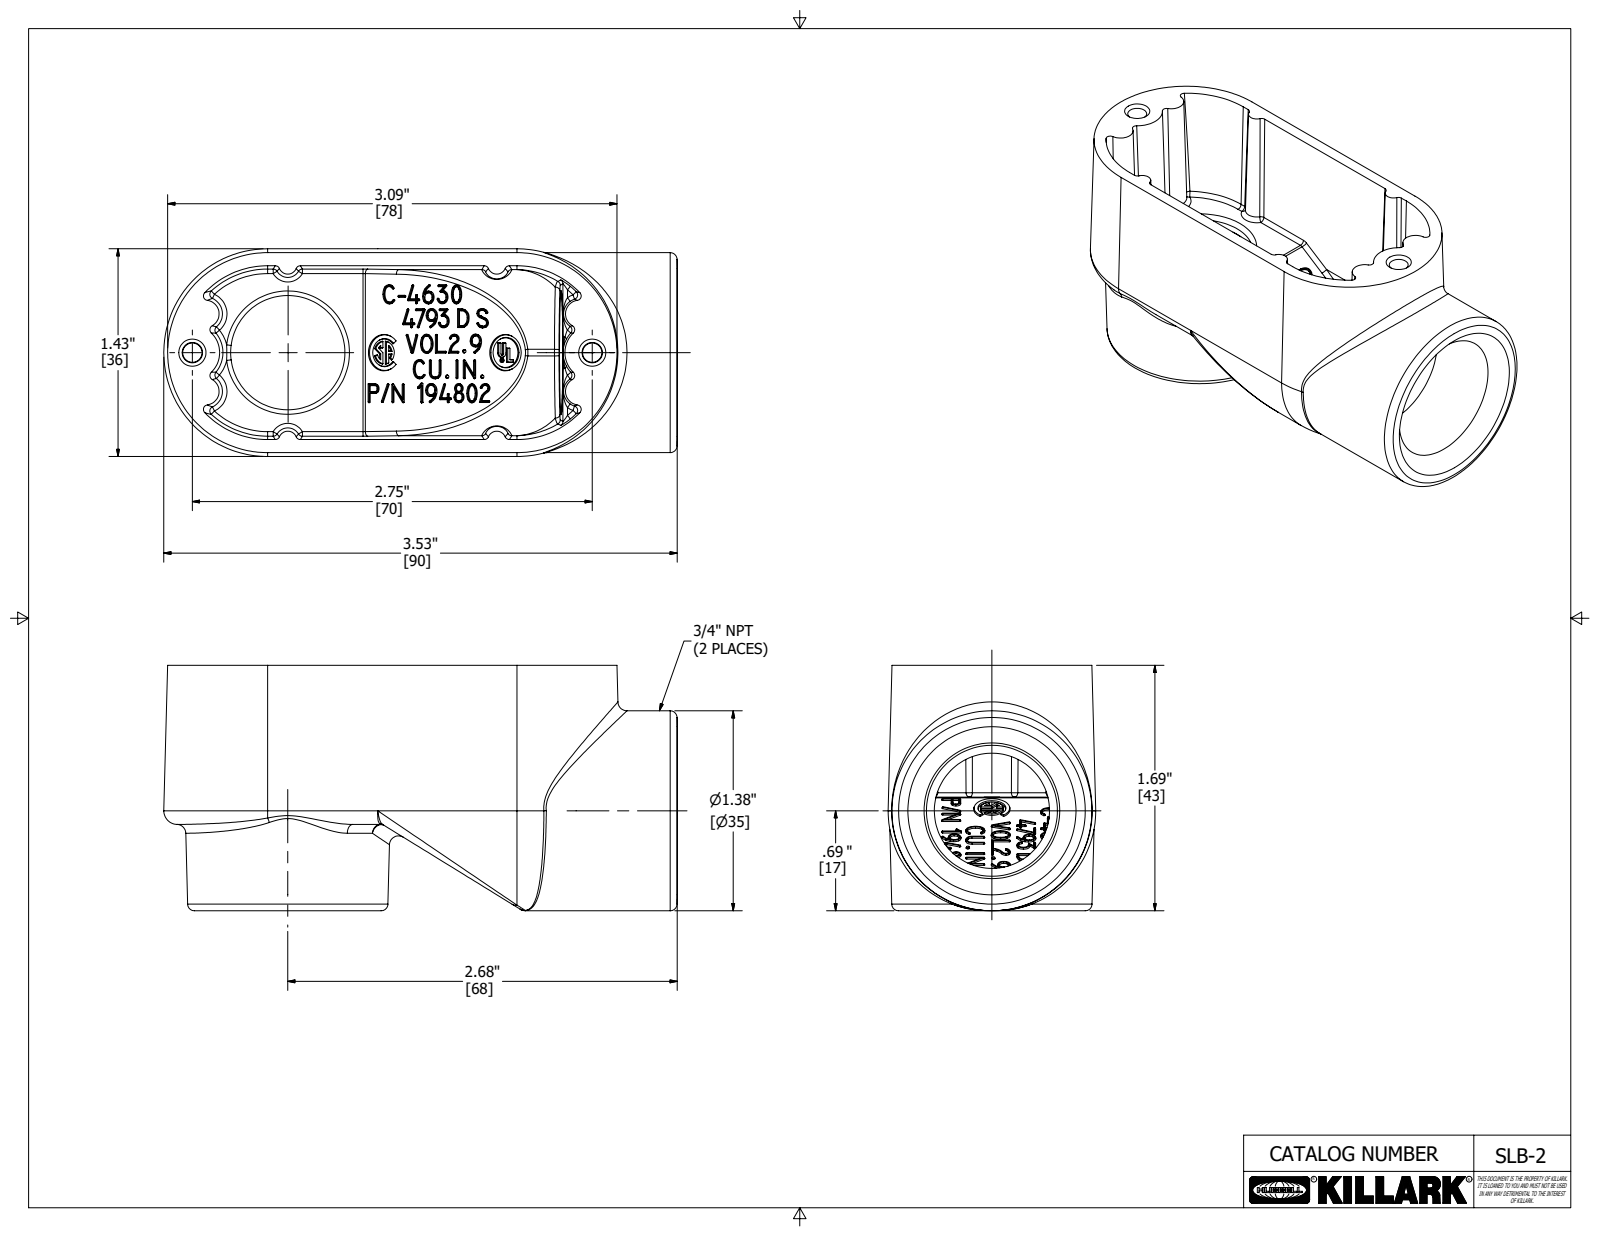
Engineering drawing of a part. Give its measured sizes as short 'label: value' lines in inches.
name: 0194802 -2
written by: Autodesk Inventor 2020 (AUTOMOTIVE_DESIGN)
unit: in
bodies: 1 solid, 777 faces (211 planar, 20 cylindrical, 546 other)
size: 3.531 × 1.688 × 1.428
volume: 2.587 in³; area: 32.59 in²
holes: 1× ⌀0.792
bosses: 1× ⌀1.375
rounds: 7× R0.031, 2× R0.094, 2× R0.594, 2× R0.687, 1× R0.297
face distances: 0.093, 0.906, 0.781, 1.687, 0.104, 0.594, 0.187, 1.094, 1.312, 0.719
